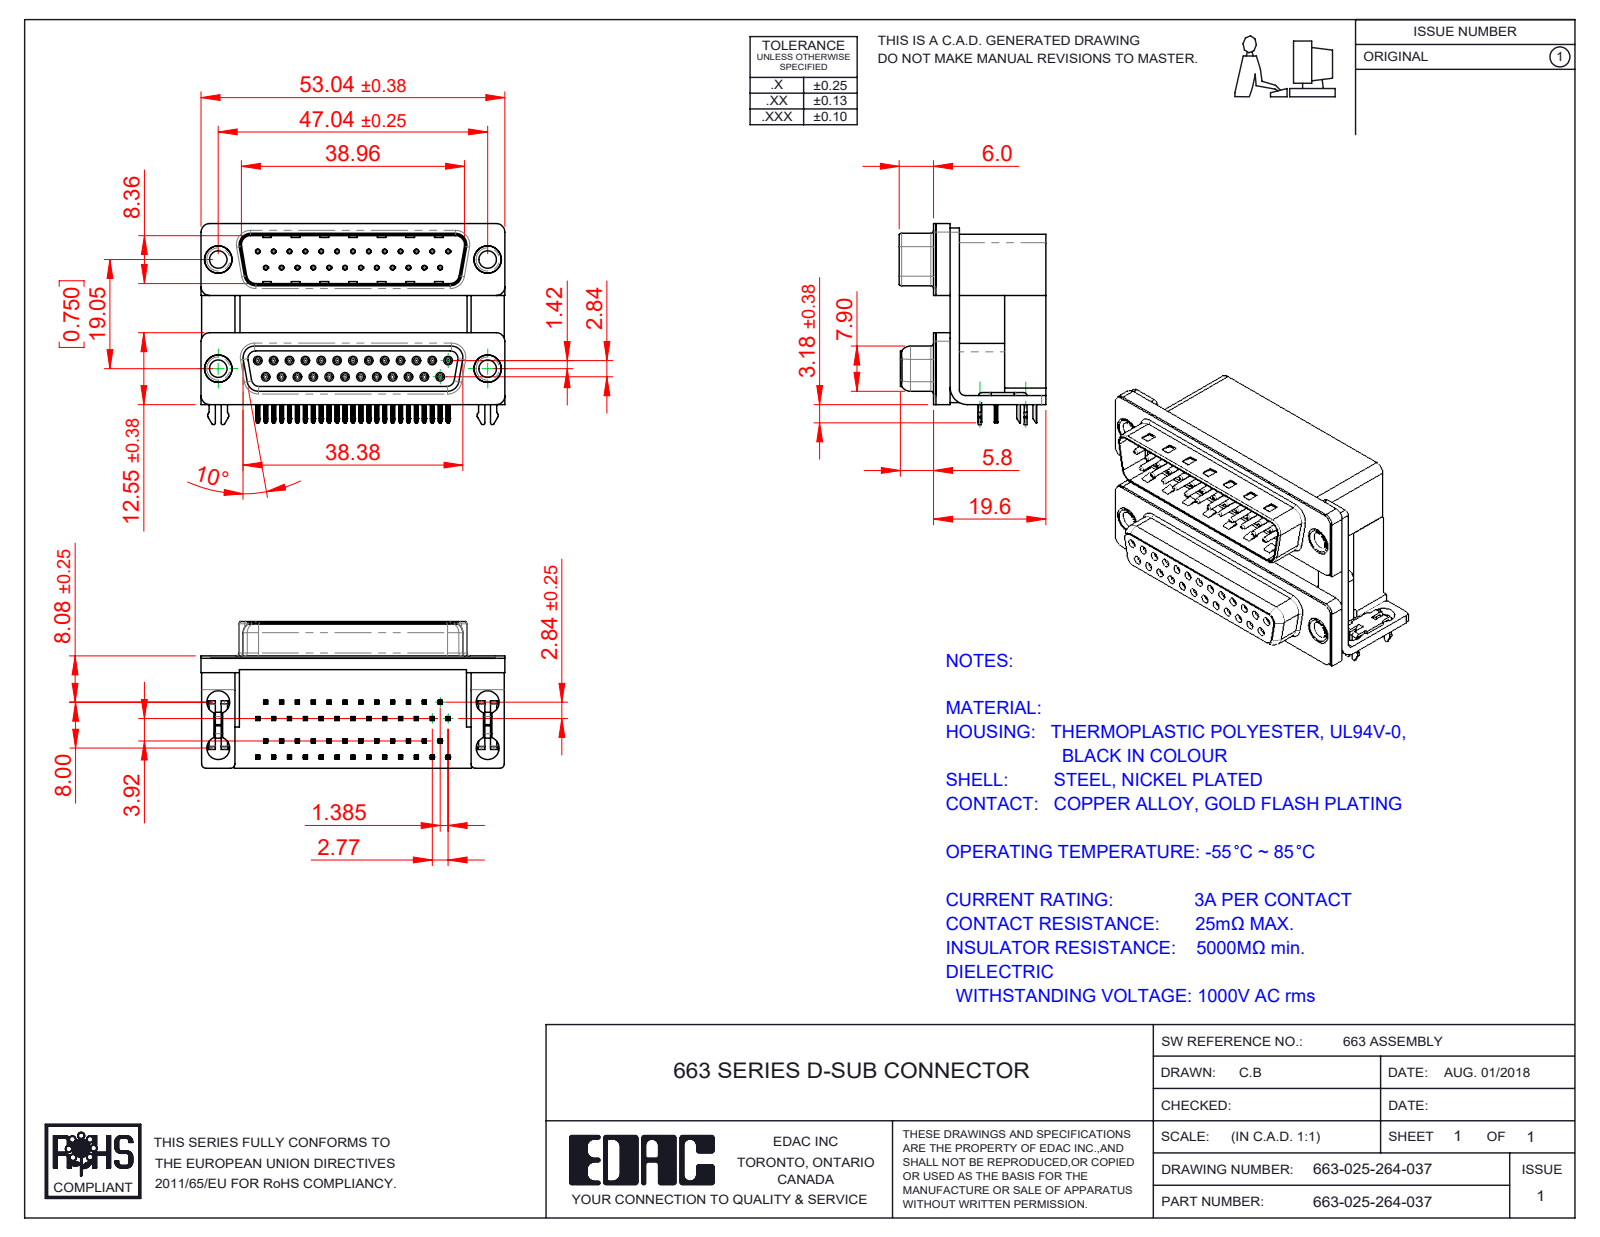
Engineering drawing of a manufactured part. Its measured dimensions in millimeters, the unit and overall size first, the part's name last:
Units: millimetres
Overall size (bounding box): 53.04 × 35.1 × 25.6
Round holes (diameter × count): ⌀0.8 ×50, ⌀0.35 ×25, ⌀0.9 ×25, ⌀4 ×8, ⌀3.05 ×4, ⌀3.5 ×4, ⌀4.8 ×4, ⌀5 ×4
Round bosses / shafts (diameter × count): ⌀1.2 ×25, ⌀0.75 ×25, ⌀4.9 ×4, ⌀4.75 ×4, ⌀3.85 ×4
Partial cylindrical surfaces — rounded edges, fillets, slot ends (radius × count): R0.1 ×202, R0.25 ×110, R0.15 ×100, R0.12 ×50, R0.35 ×50, R0.34 ×25, R0.5 ×16, R1.5 ×14
Main face-to-face distances: 19.2, 0.4, 7.2, 12, 10.69, 16.7, 9.5, 2.5, 18.71, 29.4
Hole centre spacings: 3.16, 2.77, 5.54, 11.08, 8.31, 5.03, 13.85, 7.48
Volume: 22 556 mm³ · Surface area: 24 093 mm²
Bodies: 63 solids, 6271 faces (3359 planar, 1557 cylindrical, 1355 other)
Part name (STEP PRODUCT): 663 Housing Upper_25 Contacts M; 663 Contact Bottom Upper_M; 663 Shell Receptacle_25 Contacts; 663 Housing Spacer_25 Contacts M (+8 more)
STEP written by: SolidWorks 2020 (CONFIG_CONTROL_DESIGN)
